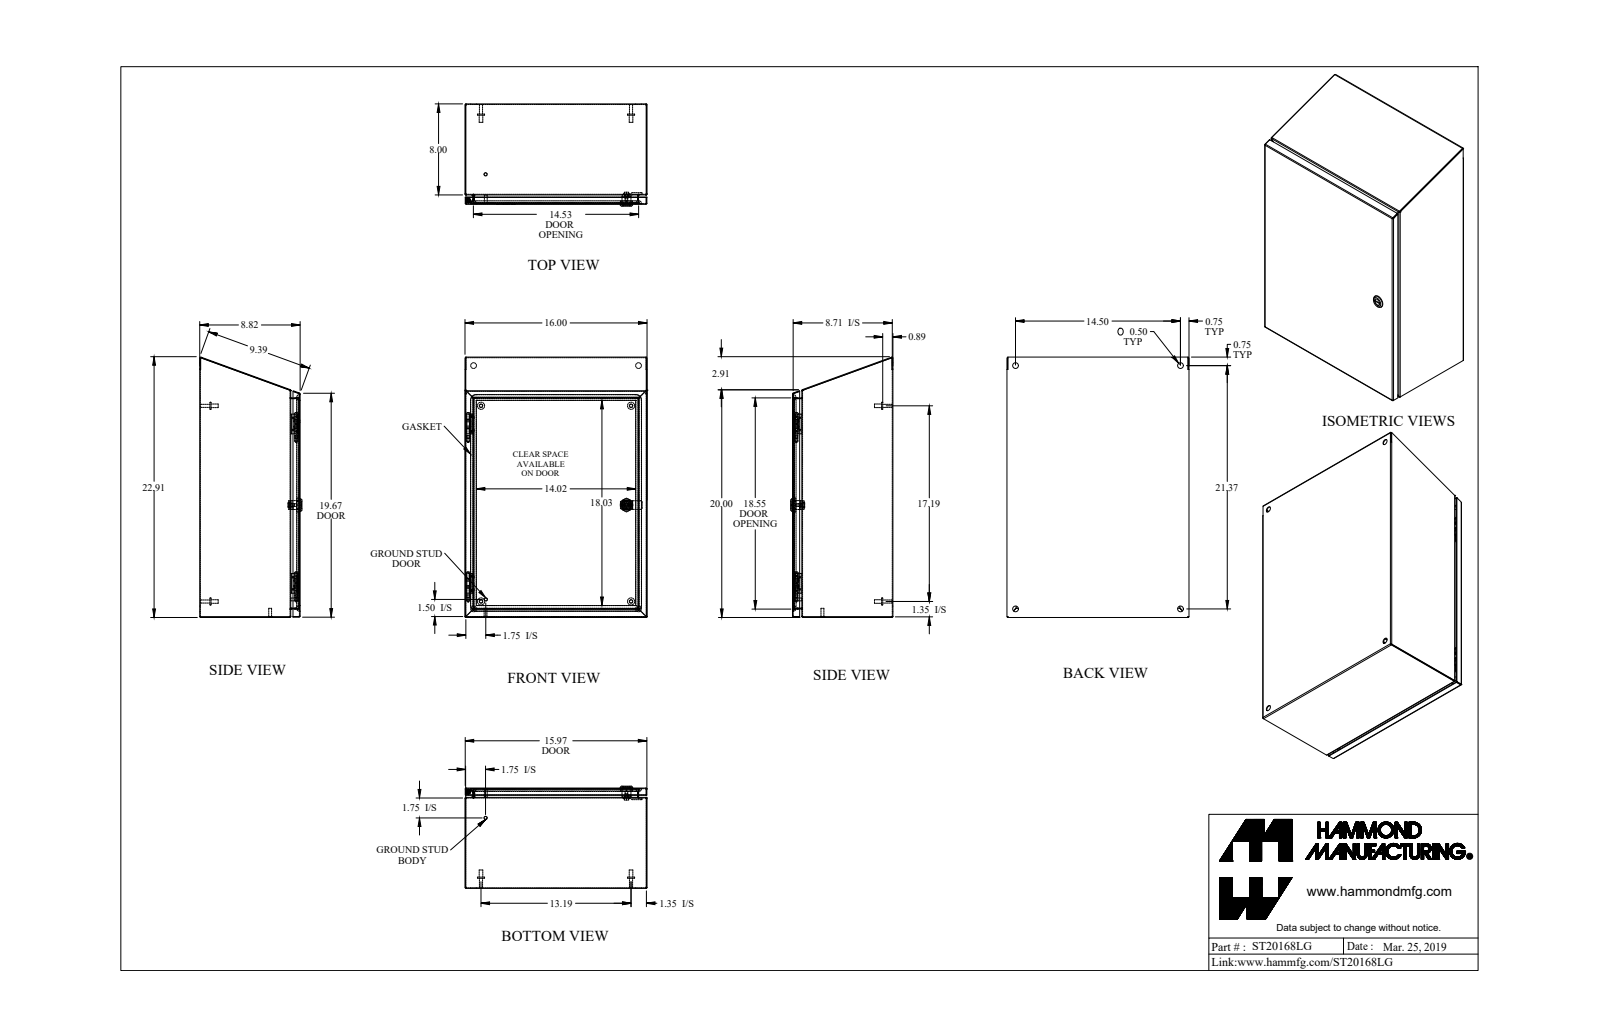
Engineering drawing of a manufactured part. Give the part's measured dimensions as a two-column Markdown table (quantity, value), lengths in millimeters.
| quantity | value |
| --- | --- |
| part name | ST20168LG |
| STEP written by | SolidWorks 2018 (AUTOMOTIVE_DESIGN) |
| units | millimeters |
| bodies | 21 solids, 632 faces (303 planar, 197 cylindrical, 132 other) |
| overall size | 581 × 406.4 × 228.1 |
| volume | 1 451 000 mm³ |
| surface area | 1 946 000 mm² |
| round holes (diameter × count) | 12.7 × 4, 4.4 × 1, 5.9 × 1, 6.1 × 1, 6.1 × 1, 15.9 × 1, 19.9 × 1 |
| round bosses / shafts (diameter × count) | 15.9 × 4, 8 × 4, 6.9 × 4, 7.1 × 2, 6.4 × 2, 27.9 × 1, 13.3 × 1, 11.6 × 1 |
| partial cylindrical surfaces (radius × count) | 0.7 × 21, 2.2 × 21, 6.4 × 11, 0.2 × 4, 1.6 × 4, 12.7 × 4, 3.2 × 2, 0.5 × 1 |
| main face-to-face distances | 1.4, 1.4, 222.6, 221.2, 405, 224.1, 222.6, 403.5, 406.4, 20.9 |
| hole center spacings | 368.3, 542.9, 656.1, 233.4, 312.2, 412.7, 461.8 |
